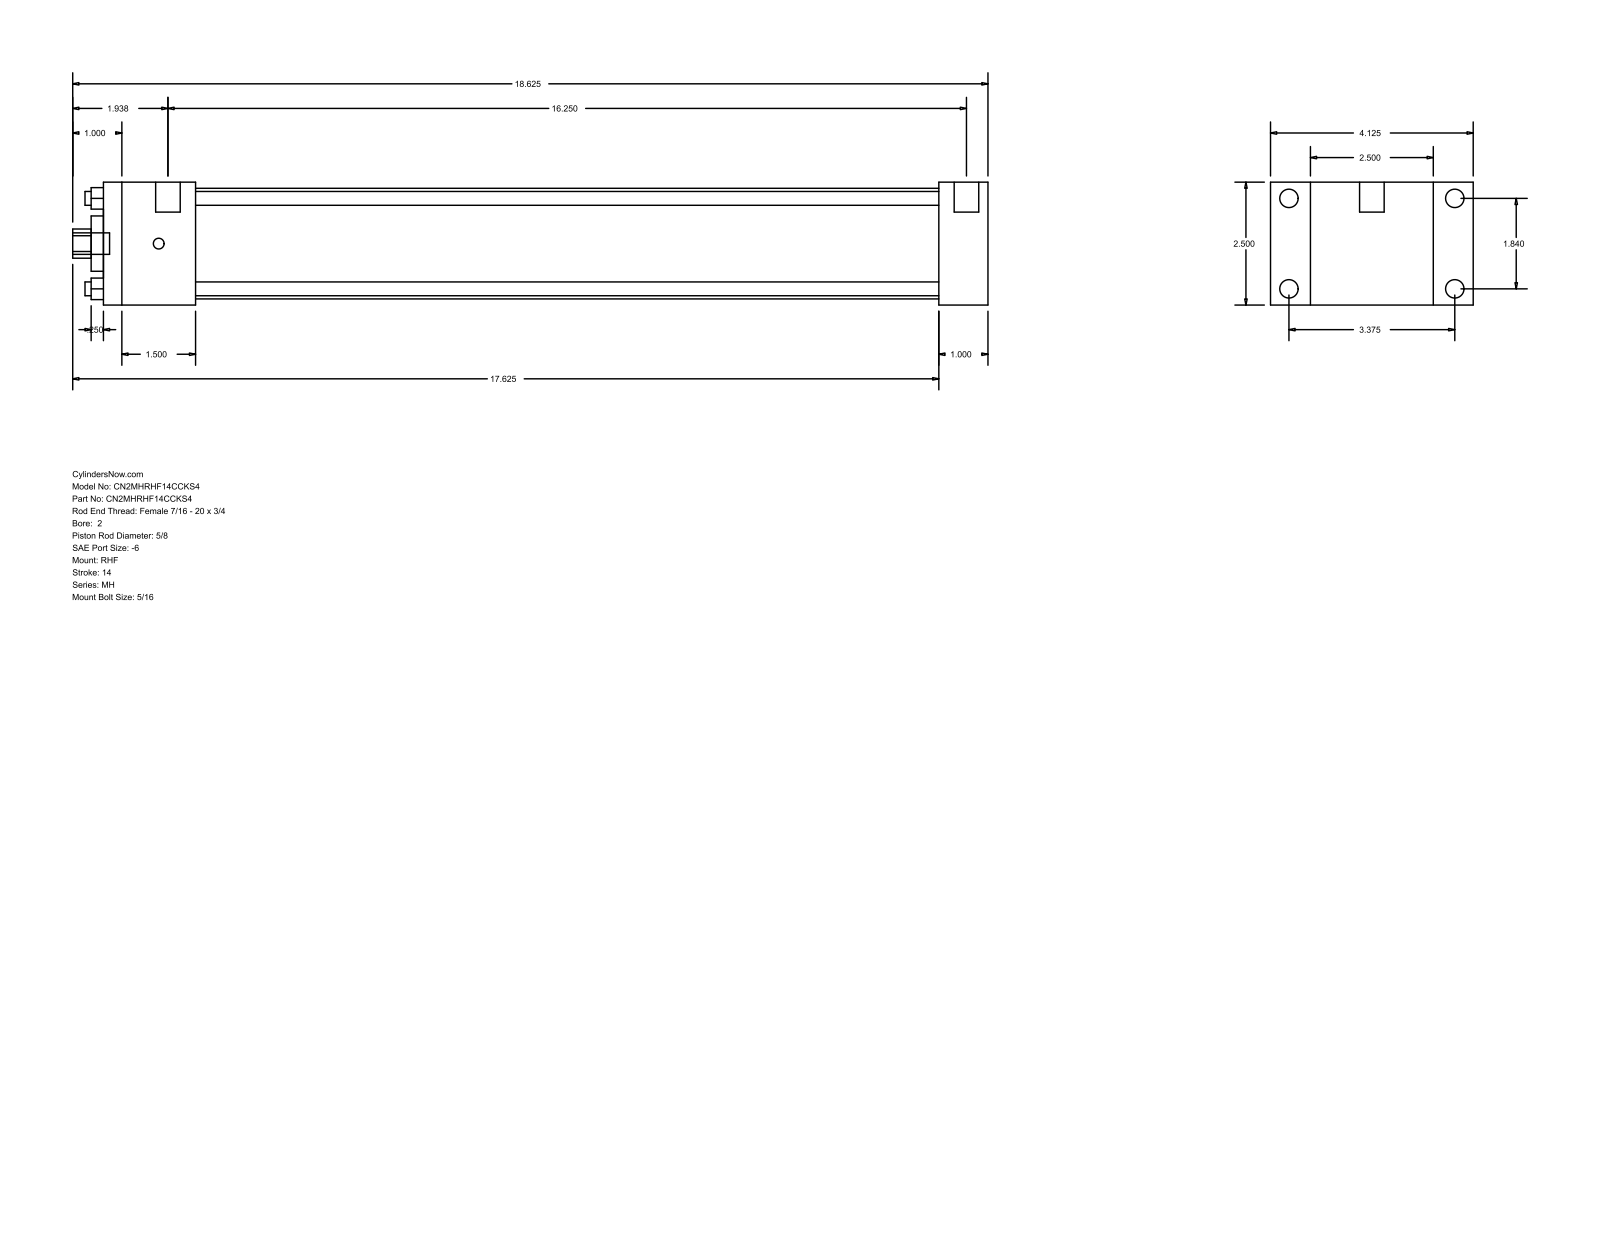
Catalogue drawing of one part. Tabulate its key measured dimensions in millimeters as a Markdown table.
| quantity | value |
| --- | --- |
| part name | MH_RHF__0200_0.625 |
| STEP written by | GSSL Pune (CONFIG_CONTROL_DESIGN) |
| units | millimeters |
| bodies | 0 solids, 88 faces (60 planar, 28 cylindrical, 0 other) |
| overall size | 473.07 × 104.78 × 63.5 |
| round holes (diameter × count) | 7.14 × 4, 15.88 × 1, 28.57 × 1, 57.15 × 1 |
| round bosses / shafts (diameter × count) | 9.53 × 4, 5.56 × 4, 12.7 × 2, 11.11 × 1 |
| partial cylindrical surfaces (radius × count) | 7.54 × 1 |
| main face-to-face distances | 63.5, 25.39, 20.64, 84.14, 431.8, 457.19, 104.78, 47.62, 384.18, 409.57 |
| hole center spacings | 33.05, 46.74, 66.1 |
